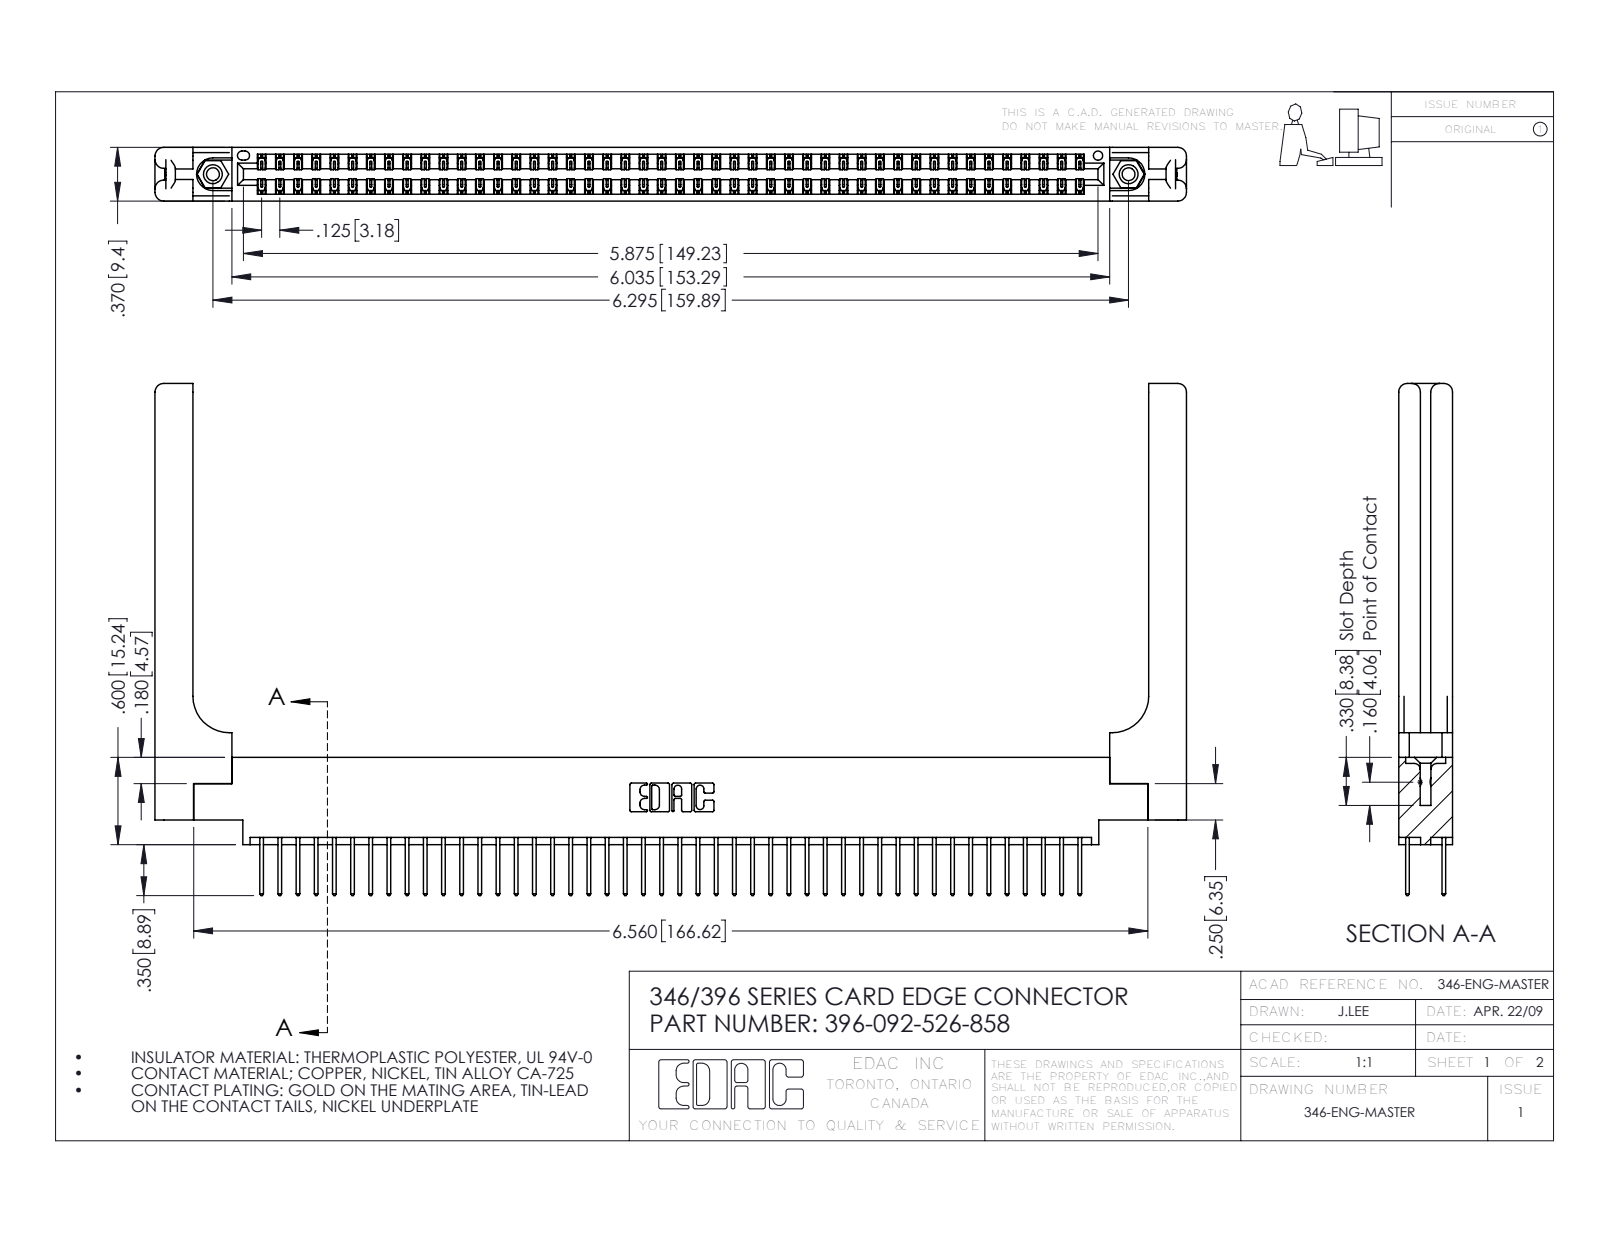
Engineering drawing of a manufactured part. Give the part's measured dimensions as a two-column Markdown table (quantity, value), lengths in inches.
| quantity | value |
| --- | --- |
| part name | 396-092-526-858; 345-292-001_345-293-126; 346-220-058_345-220-058; 346 Part_0.170 Offset - 0.156 Dia-TH (+1 more) |
| STEP written by | SolidWorks 2016 (CONFIG_CONTROL_DESIGN) |
| units | inches |
| bodies | 97 solids, 5166 faces (3448 planar, 1658 cylindrical, 60 other) |
| overall size | 7.091 × 3.52 × 0.37 |
| volume | 1.531 in³ |
| surface area | 46.61 in² |
| round holes (diameter × count) | 0.089 × 2, 0.125 × 2, 0.156 × 2, 0.064 × 1 |
| round bosses / shafts (diameter × count) | 0.155 × 2 |
| partial cylindrical surfaces (radius × count) | 0.006 × 138, 0.01 × 92, 0.01 × 22, 0.06 × 16, 0.007 × 6, 0.031 × 6, 0.026 × 3, 0.014 × 2 |
| main face-to-face distances | 0.048, 0.322, 0.37, 0.072, 0.25, 0.025, 0.298, 0.148, 0.15, 0.275 |
| hole center spacings | 0.246, 6.086, 6.295 |
